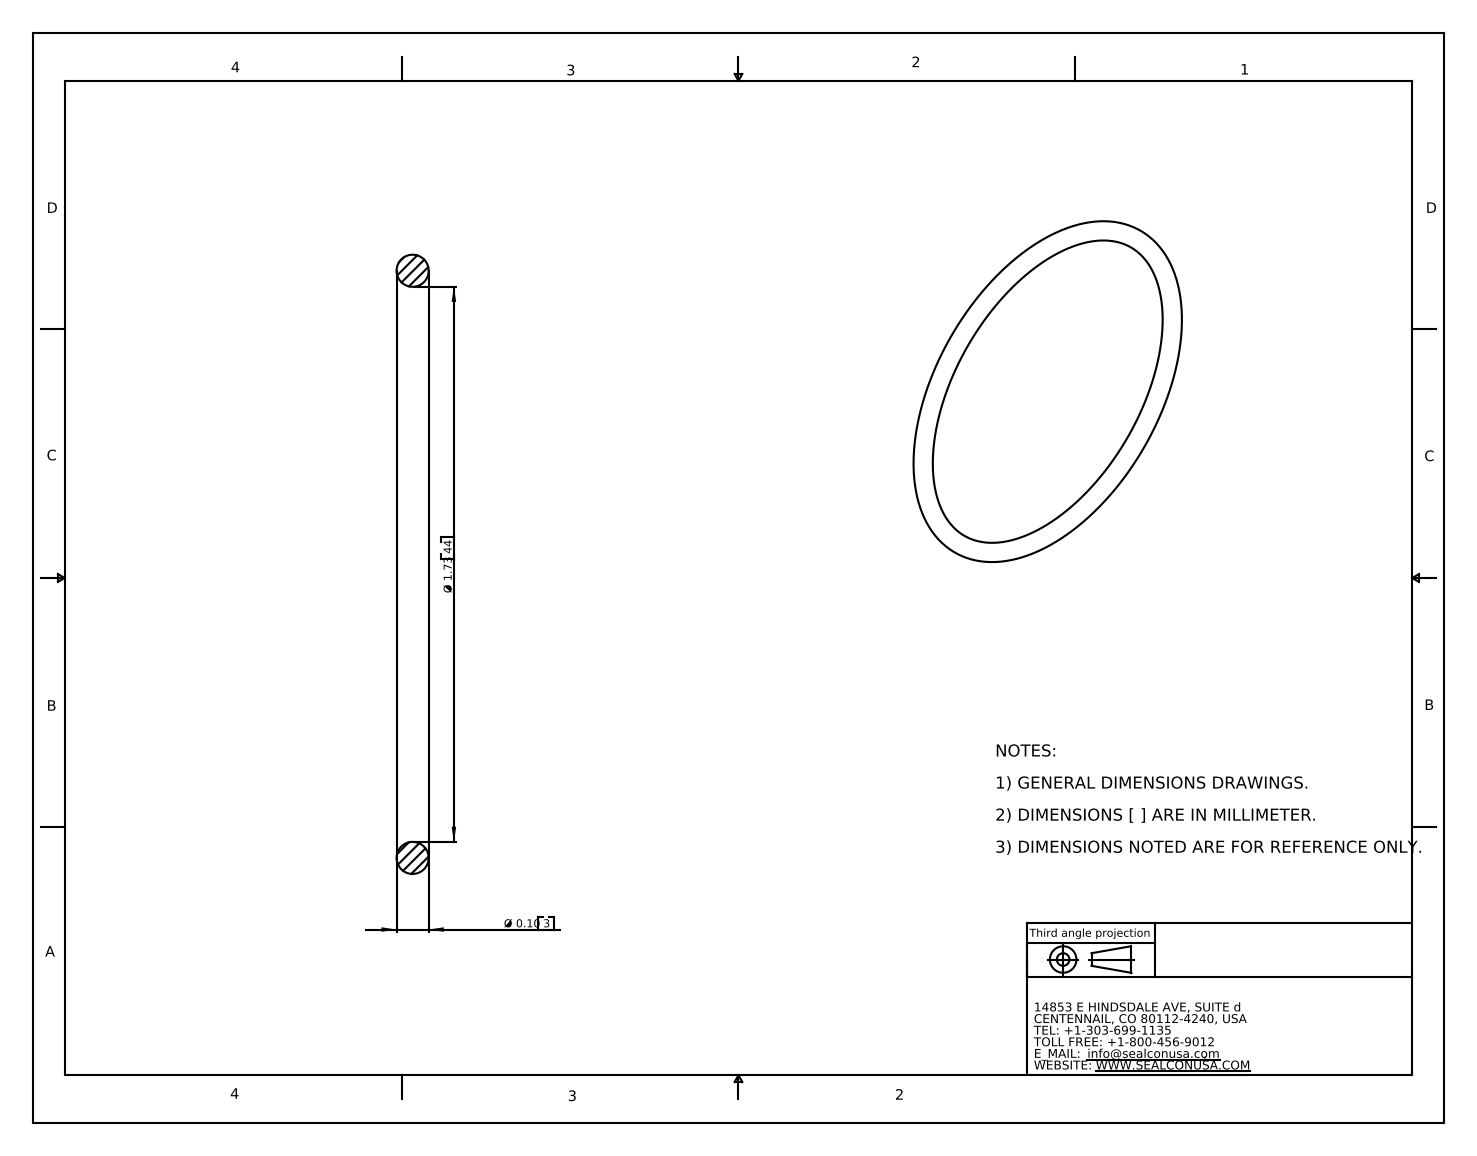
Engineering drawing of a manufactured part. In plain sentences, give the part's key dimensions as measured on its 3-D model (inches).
The part is named "OR-64-BN". Its 3-D file was written by "SolidWorks 2007 (CONFIG_CONTROL_DESIGN)". It is 1 solid with 4 faces: 0 planar, 0 cylindrical and 4 other. Overall it measures 1.93 by 1.93 by 0.1 inches. Its volume is 0.045 cubic inches and its surface area 1.806 square inches.
